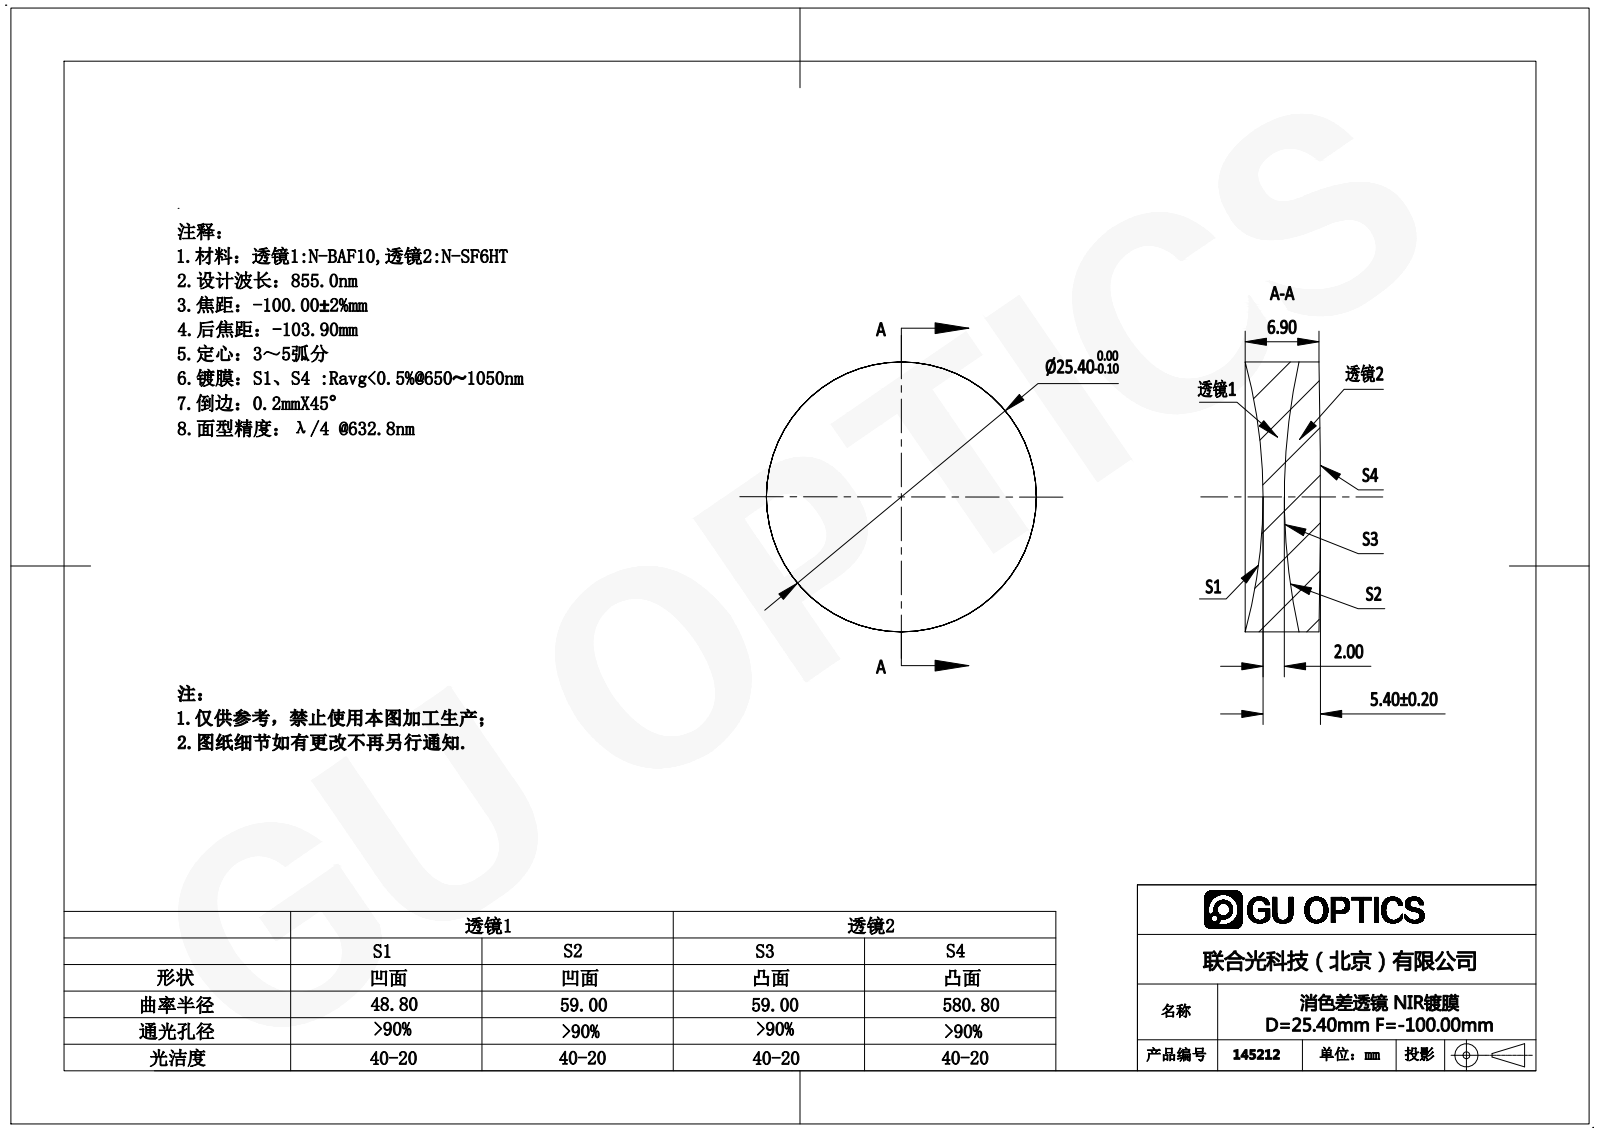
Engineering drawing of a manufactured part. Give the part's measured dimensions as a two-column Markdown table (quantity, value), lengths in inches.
| quantity | value |
| --- | --- |
| part name | 145212 |
| STEP written by | SolidWorks 2016 (AUTOMOTIVE_DESIGN) |
| units | inches |
| bodies | 2 solids, 12 faces (0 planar, 4 cylindrical, 8 other) |
| overall size | 1 × 1 × 0.279 |
| volume | 0.191 in³ |
| surface area | 4.033 in² |
| round bosses / shafts (diameter × count) | 1 × 1 |
